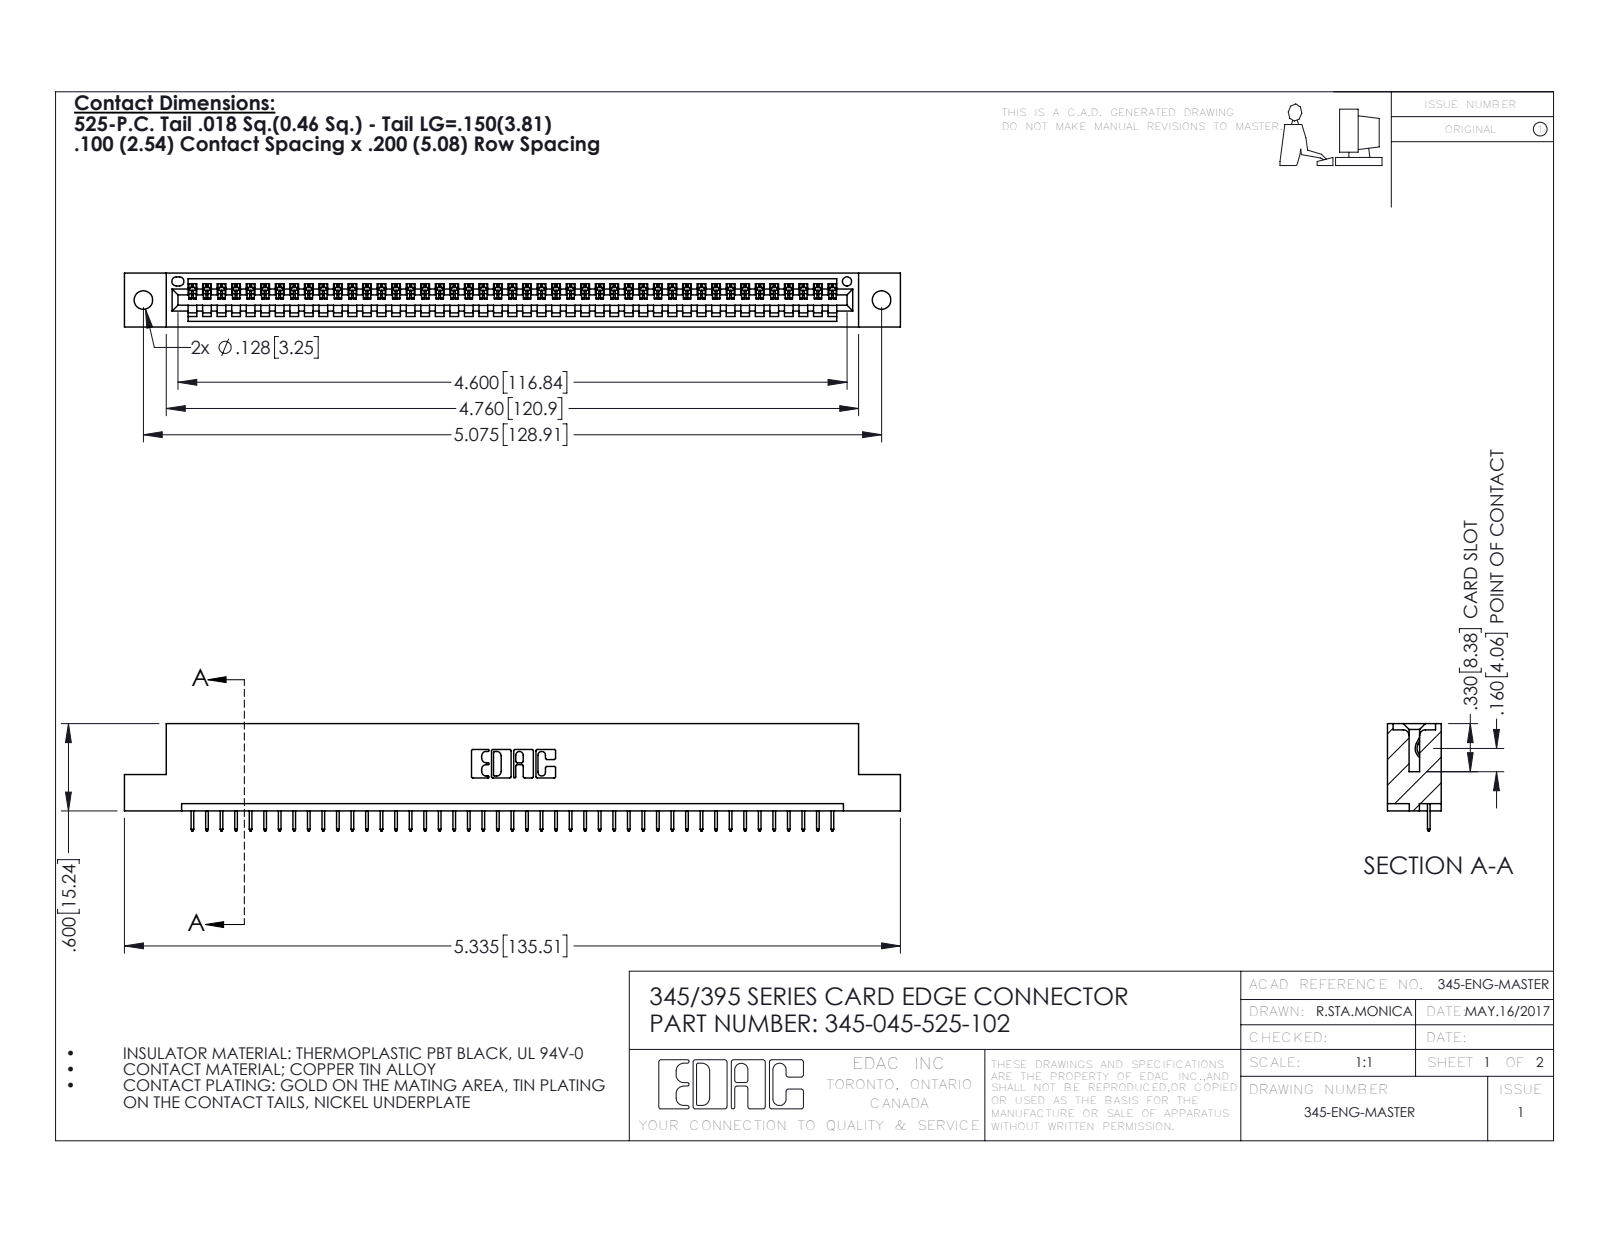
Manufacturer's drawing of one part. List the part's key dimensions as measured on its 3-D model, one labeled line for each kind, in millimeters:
Part name (STEP PRODUCT): 345 Part_Flush Mounting Lugs - 0.128 Dia; 345-292-001_345-293-125; 345-045-525-102
STEP written by: SolidWorks 2020 (CONFIG_CONTROL_DESIGN)
Units: millimetres
Bodies: 46 solids, 2916 faces (2150 planar, 766 cylindrical, 0 other)
Overall size (bounding box): 135.5 × 18.7 × 9.4
Volume: 12 700 mm³ · Surface area: 16 000 mm²
Round holes (diameter × count): ⌀3.3 ×2, ⌀1.6 ×1
Partial cylindrical surfaces — rounded edges, fillets, slot ends (radius × count): R0.2 ×90, R0.3 ×22, R0.2 ×6, R0.8 ×6, R0.7 ×3, R0.8 ×2, R1 ×2, R0.4 ×1
Main face-to-face distances: 7.6, 1.8, 9.4, 5.1, 2.5, 6.9, 0.6, 5.7, 1.8, 3.8
Hole centre spacings: 6.9, 122.9, 128.9
